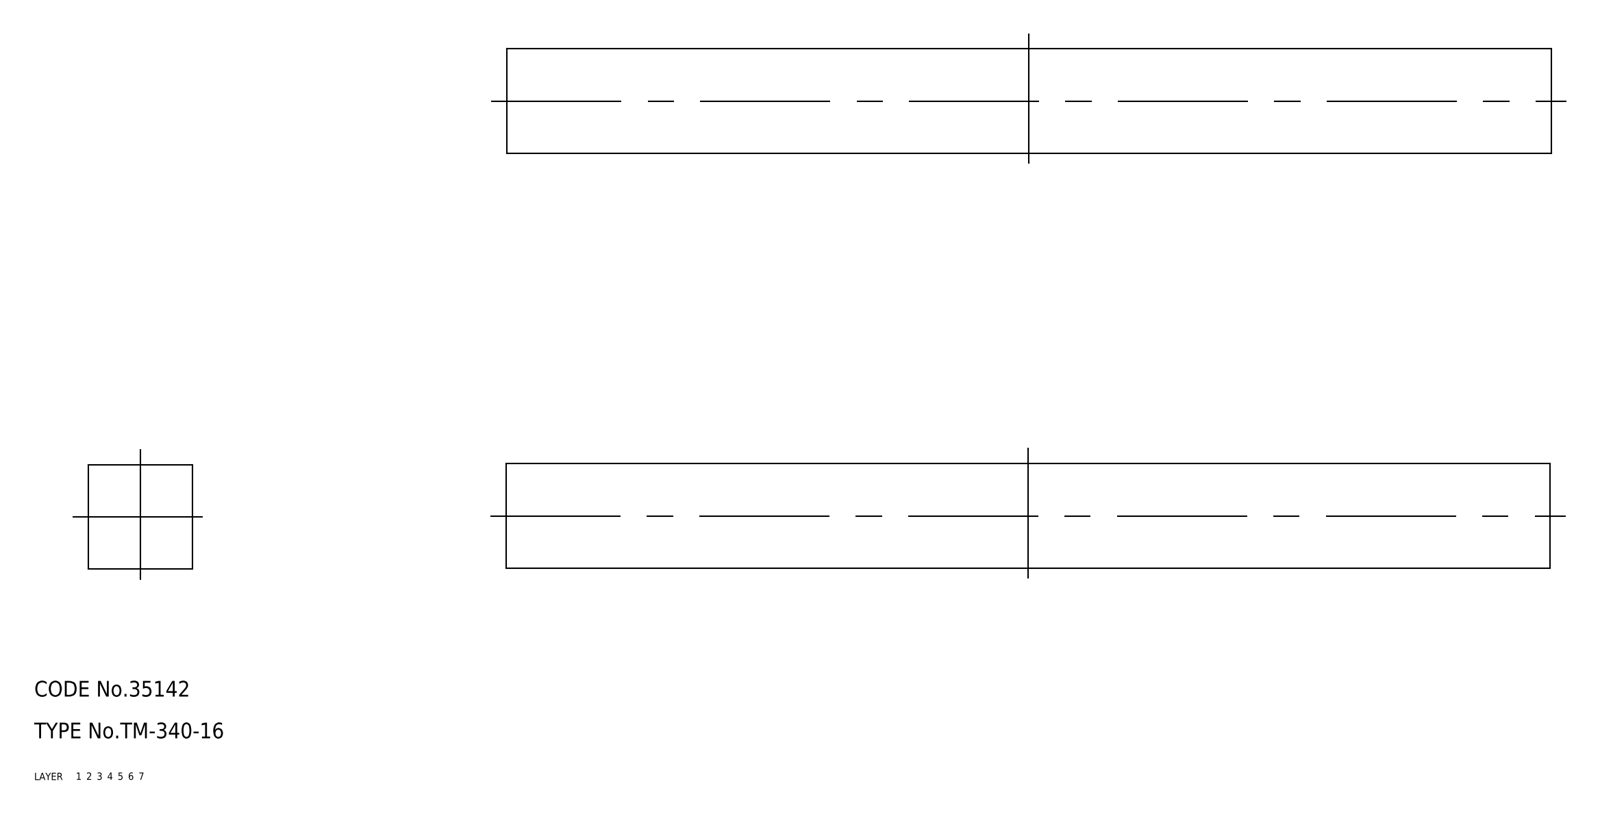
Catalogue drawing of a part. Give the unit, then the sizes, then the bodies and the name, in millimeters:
Units: millimetres
Overall size (bounding box): 200 × 20 × 20
Main face-to-face distances: 20, 200
Volume: 80 000 mm³ · Surface area: 16 800 mm²
Bodies: 1 solid, 6 faces (6 planar, 0 cylindrical, 0 other)
Part name (STEP PRODUCT): TM_340_16; rubber foam
STEP written by: SolidWorks 2015 (AUTOMOTIVE_DESIGN)
